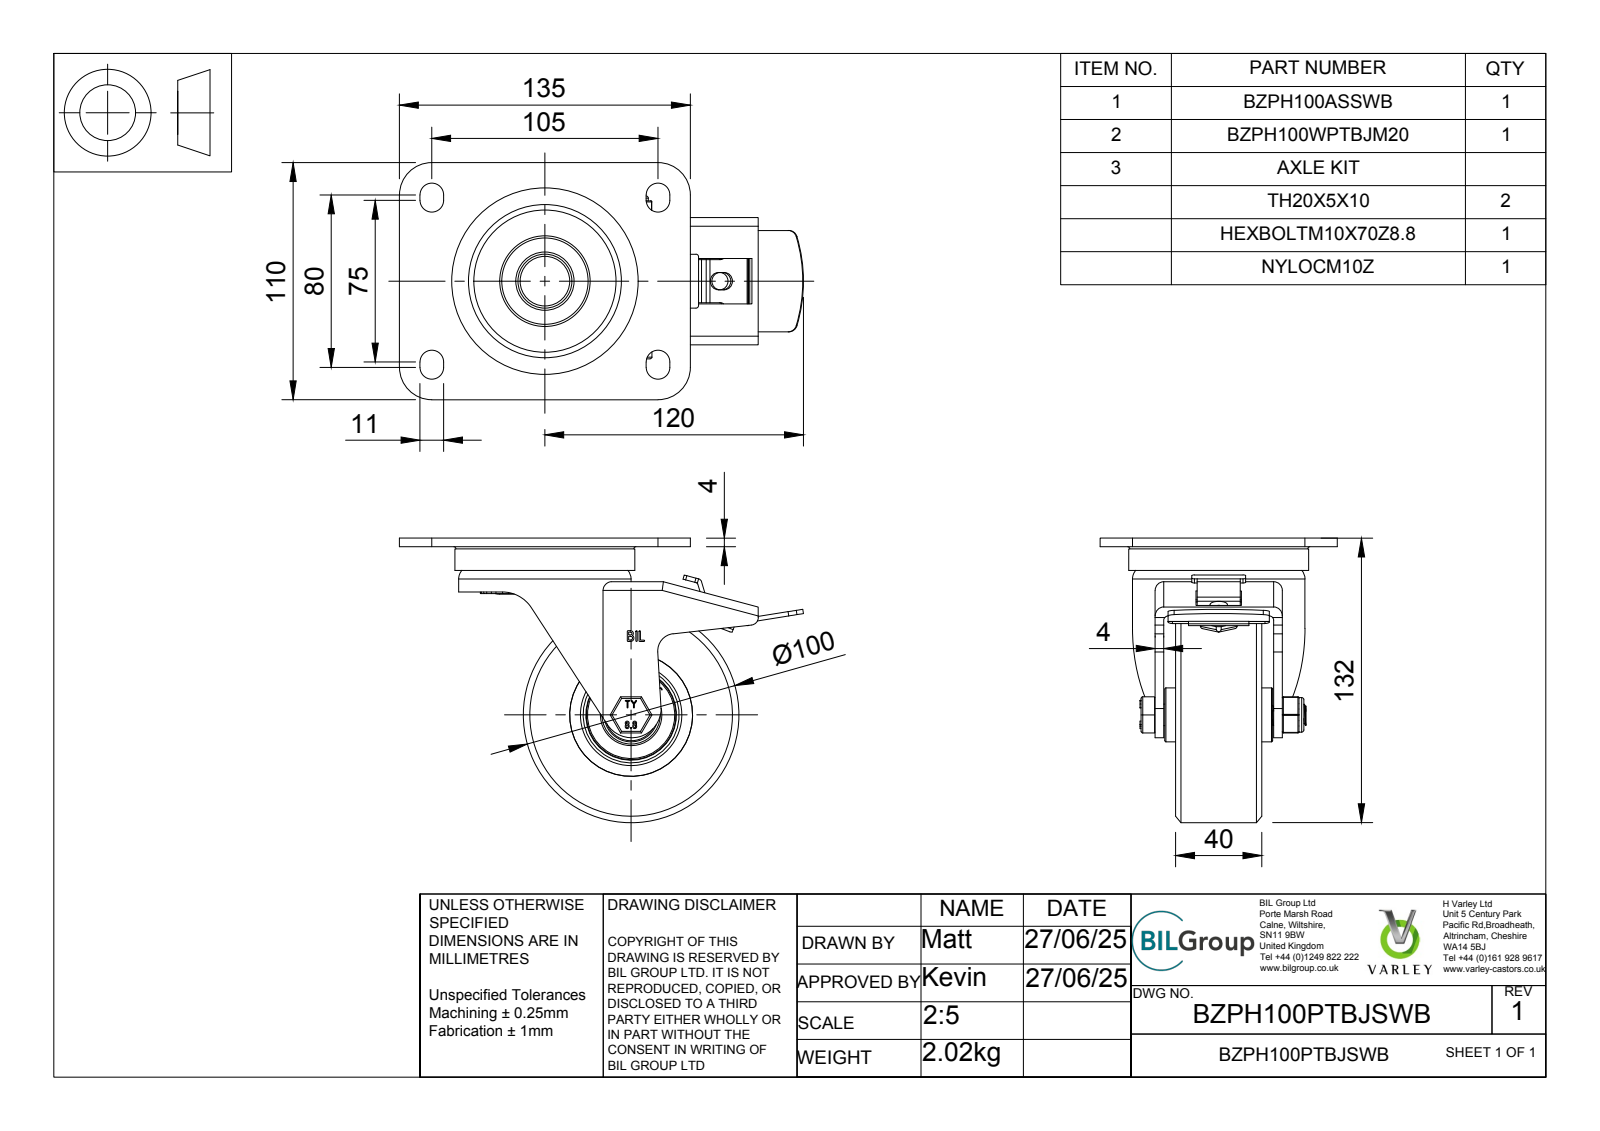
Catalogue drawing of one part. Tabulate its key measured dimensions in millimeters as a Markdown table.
| quantity | value |
| --- | --- |
| part name | BZPH100PTBJSWB v3; BZPH100ASSWB v1; ZINC PLATED, PRESSED STEEL TOP PLATE; ZINC PLATED, PRESSED STEEL FORKS (+8 more) |
| STEP written by | Autodesk Translation Framework v14.10.0.0 (AUTOMOTIVE_DESIGN) |
| units | millimeters |
| bodies | 41 solids, 1593 faces (822 planar, 328 cylindrical, 443 other) |
| overall size | 187.5 × 132 × 110 |
| volume | 473 709 mm³ |
| surface area | 187 440 mm² |
| round holes (diameter × count) | 8 × 1, 10 × 1, 10.2 × 1, 10.5 × 1, 12 × 1, 20 × 1, 26 × 1, 28 × 1, 28.5 × 1, 30 × 1, 41.5 × 1, 42 × 1 |
| round bosses / shafts (diameter × count) | 25 × 2, 100 × 1, 83.5 × 1, 80 × 1, 60 × 1, 51 × 1, 40.5 × 1, 40 × 1 |
| partial cylindrical surfaces (radius × count) | 0.5 × 27, 4 × 22, 2 × 15, 6 × 13, 0.75 × 10, 5.5 × 8, 1.5 × 7, 1.25 × 4 |
| main face-to-face distances | 4, 13, 9, 26, 40, 5.5, 55, 9.5, 49.5, 1 |
